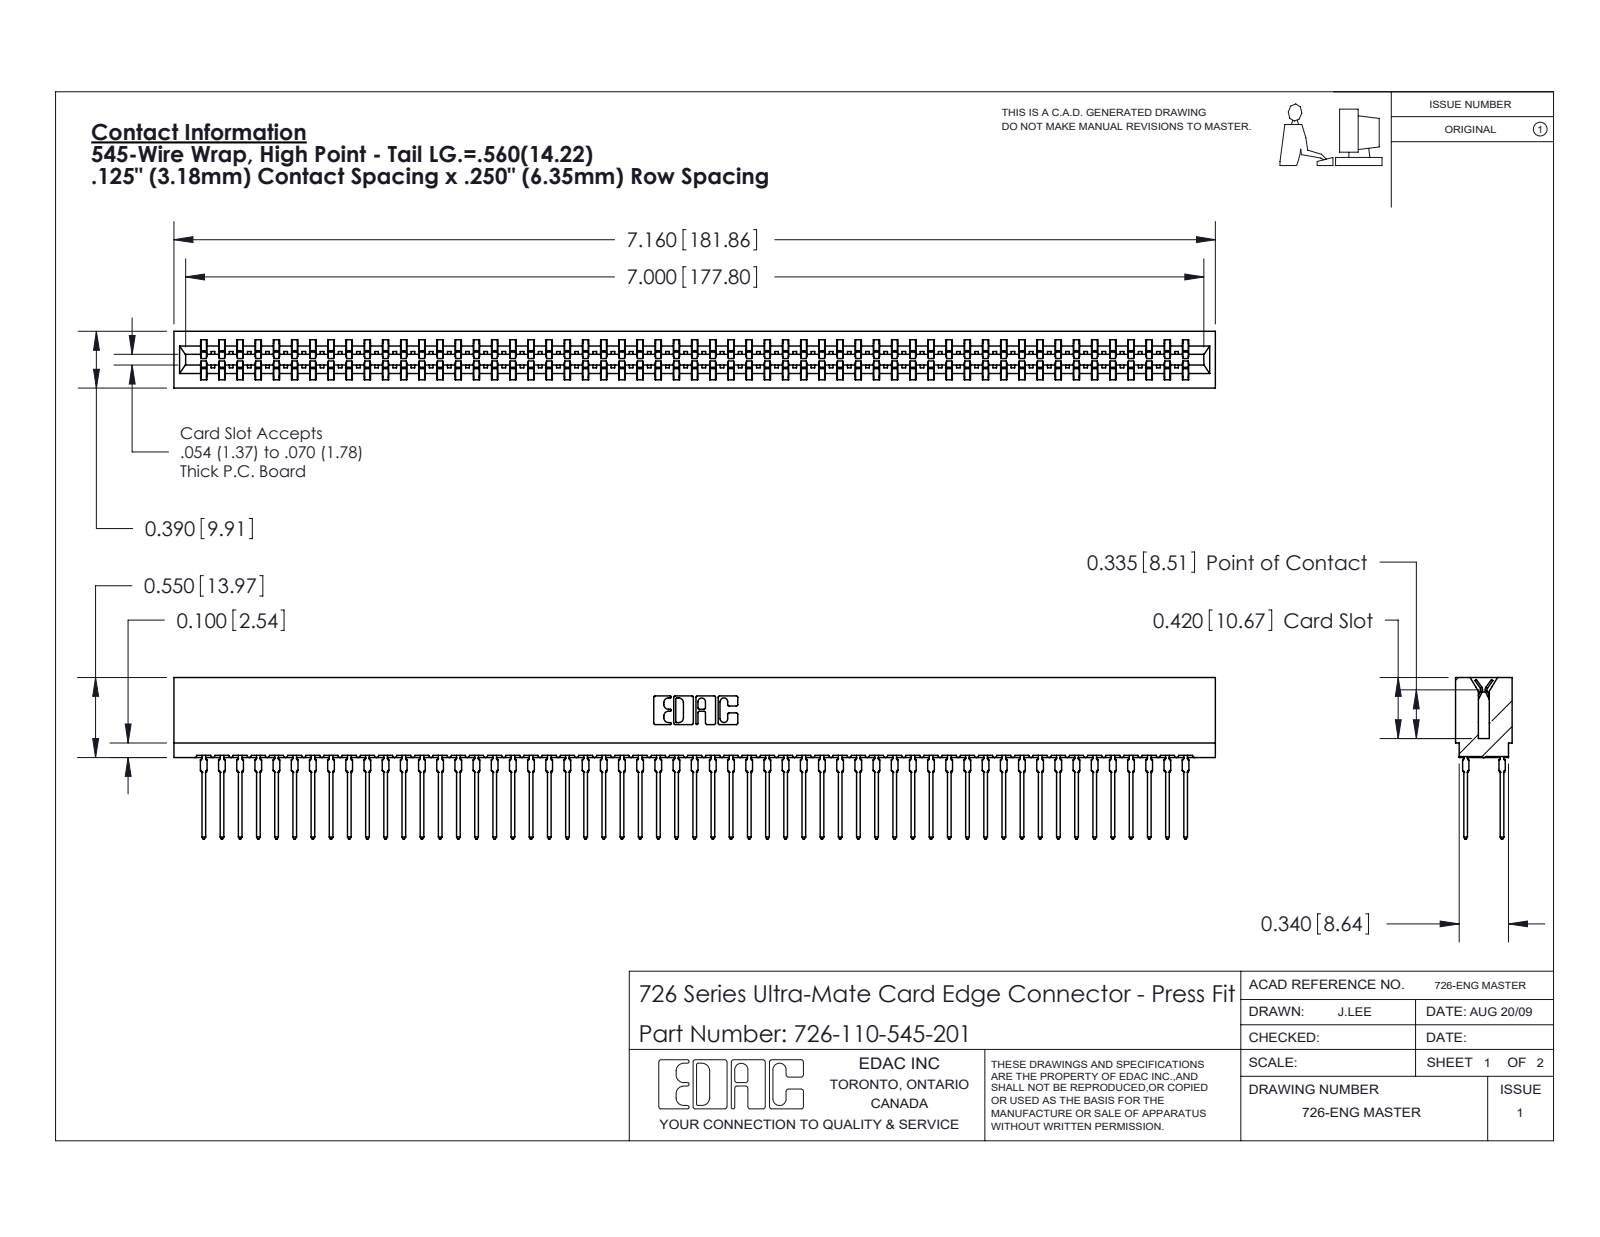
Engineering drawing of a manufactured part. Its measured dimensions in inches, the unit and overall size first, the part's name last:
Units: inches
Overall size (bounding box): 7.16 × 1.109 × 0.39
Partial cylindrical surfaces — rounded edges, fillets, slot ends (radius × count): R0.021 ×220, R0.015 ×56, R0.01 ×22, R0.005 ×8, R0.011 ×8, R0.007 ×6, R0.031 ×6, R0.026 ×3
Main face-to-face distances: 0.057, 0.333, 0.025, 0.307, 0.25, 0.39, 0.083, 0.275, 0.365, 0.032
Volume: 1.04 in³ · Surface area: 47.11 in²
Bodies: 111 solids, 9942 faces (5115 planar, 1967 cylindrical, 2860 other)
Part name (STEP PRODUCT): 726-110-545-201; 726 Part_.515 Slot Depth - 01; 746-292-001_545
STEP written by: SolidWorks 2020 (CONFIG_CONTROL_DESIGN)
